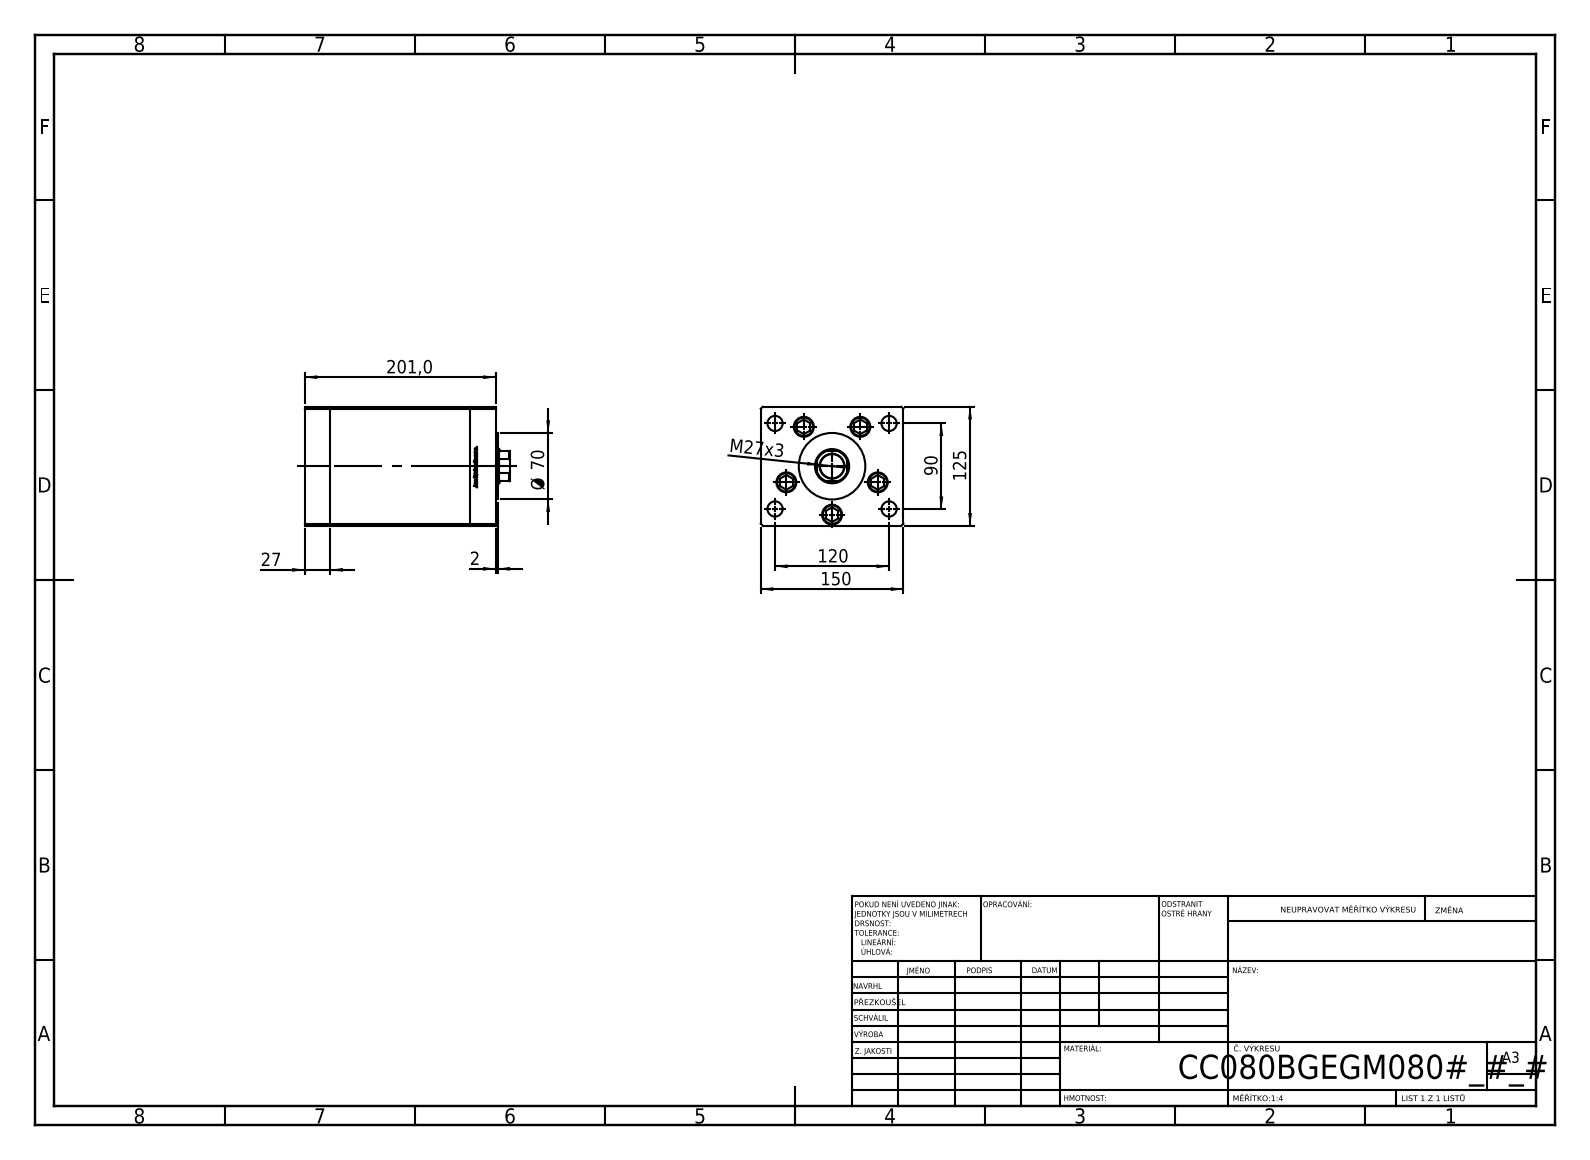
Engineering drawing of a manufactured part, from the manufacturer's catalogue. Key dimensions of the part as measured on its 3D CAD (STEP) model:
Part name (STEP PRODUCT): V220C_B MIDDLE; V220C BACK_B; V220C_FRONT_B; ALLEN BOLT (+1 more)
STEP written by: SolidWorks 2019 (CONFIG_CONTROL_DESIGN)
Units: millimetres
Bodies: 14 solids, 1185 faces (464 planar, 147 cylindrical, 574 other)
Overall size (bounding box): 216 × 150 × 125
Volume: 3 289 000 mm³ · Surface area: 349 130 mm²
Round holes (diameter × count): ⌀17.5 ×5, ⌀21 ×5, ⌀16 ×4, ⌀2 ×2, ⌀13.16 ×2, ⌀25.5 ×1, ⌀36 ×1
Round bosses / shafts (diameter × count): ⌀8 ×5, ⌀80 ×1, ⌀70 ×1
Partial cylindrical surfaces — rounded edges, fillets, slot ends (radius × count): R0.93 ×2, R17.5 ×1
Main face-to-face distances: 27, 174, 147, 125, 150, 33.5, 201, 6.5, 140.5, 167.5
Hole centre spacings: 51, 75, 30.43, 30.48, 58.89, 60.3, 61.25, 63.14
